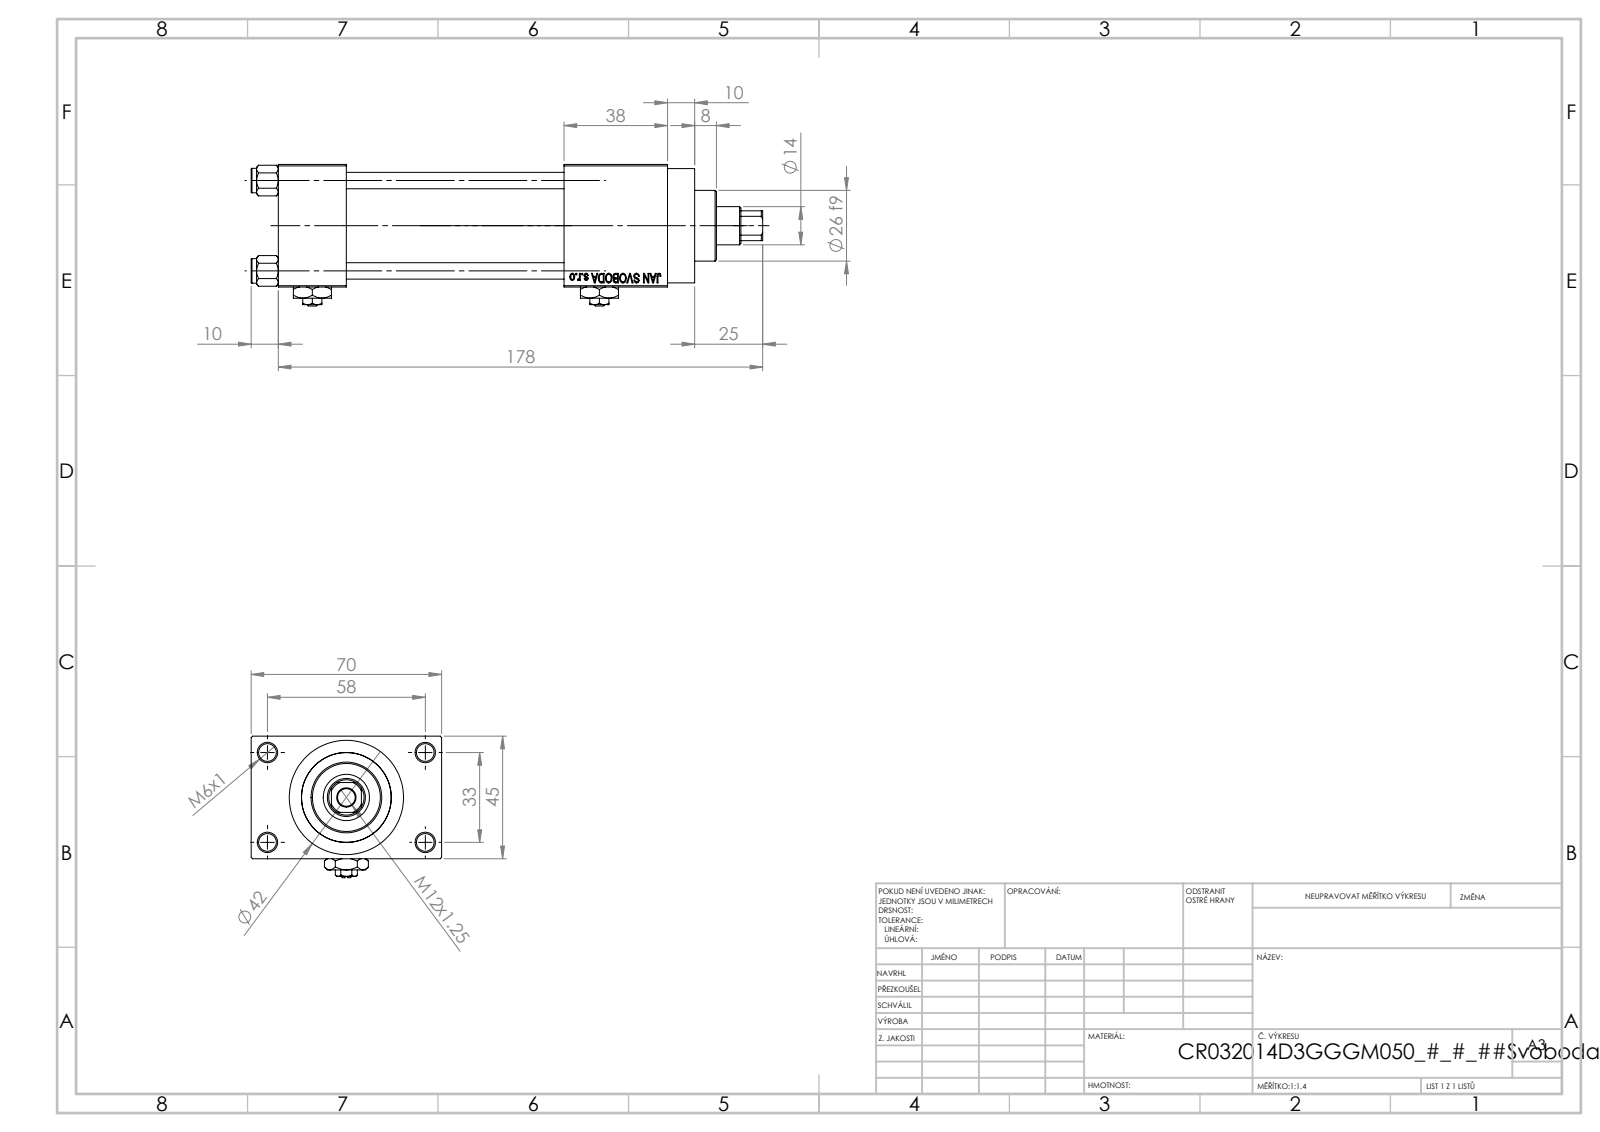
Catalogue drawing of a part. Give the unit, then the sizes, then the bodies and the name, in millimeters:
Units: millimetres
Overall size (bounding box): 188 × 70 × 52
Round holes (diameter × count): ⌀6.5 ×5, ⌀6 ×4, ⌀7 ×2, ⌀13.16 ×2, ⌀20 ×2, ⌀14 ×1, ⌀17 ×1, ⌀24 ×1, ⌀32 ×1, ⌀33 ×1
Round bosses / shafts (diameter × count): ⌀9 ×4, ⌀42 ×1, ⌀38 ×1, ⌀26 ×1
Partial cylindrical surfaces — rounded edges, fillets, slot ends (radius × count): R6.5 ×1
Main face-to-face distances: 45, 25, 12.5, 57.5, 80, 105, 118, 70, 38, 143
Hole centre spacings: 12.4, 23.48, 33.2, 33.37, 35.35, 45.6, 56.35, 33
Volume: 248 605 mm³ · Surface area: 86 795 mm²
Bodies: 13 solids, 1202 faces (542 planar, 100 cylindrical, 560 other)
Part name (STEP PRODUCT): NUT_M5_D; V215CR_D_Body; V215CR_VCP_D; V215CR_D_TYCINKA (+2 more)
STEP written by: SolidWorks 2019 (CONFIG_CONTROL_DESIGN)
